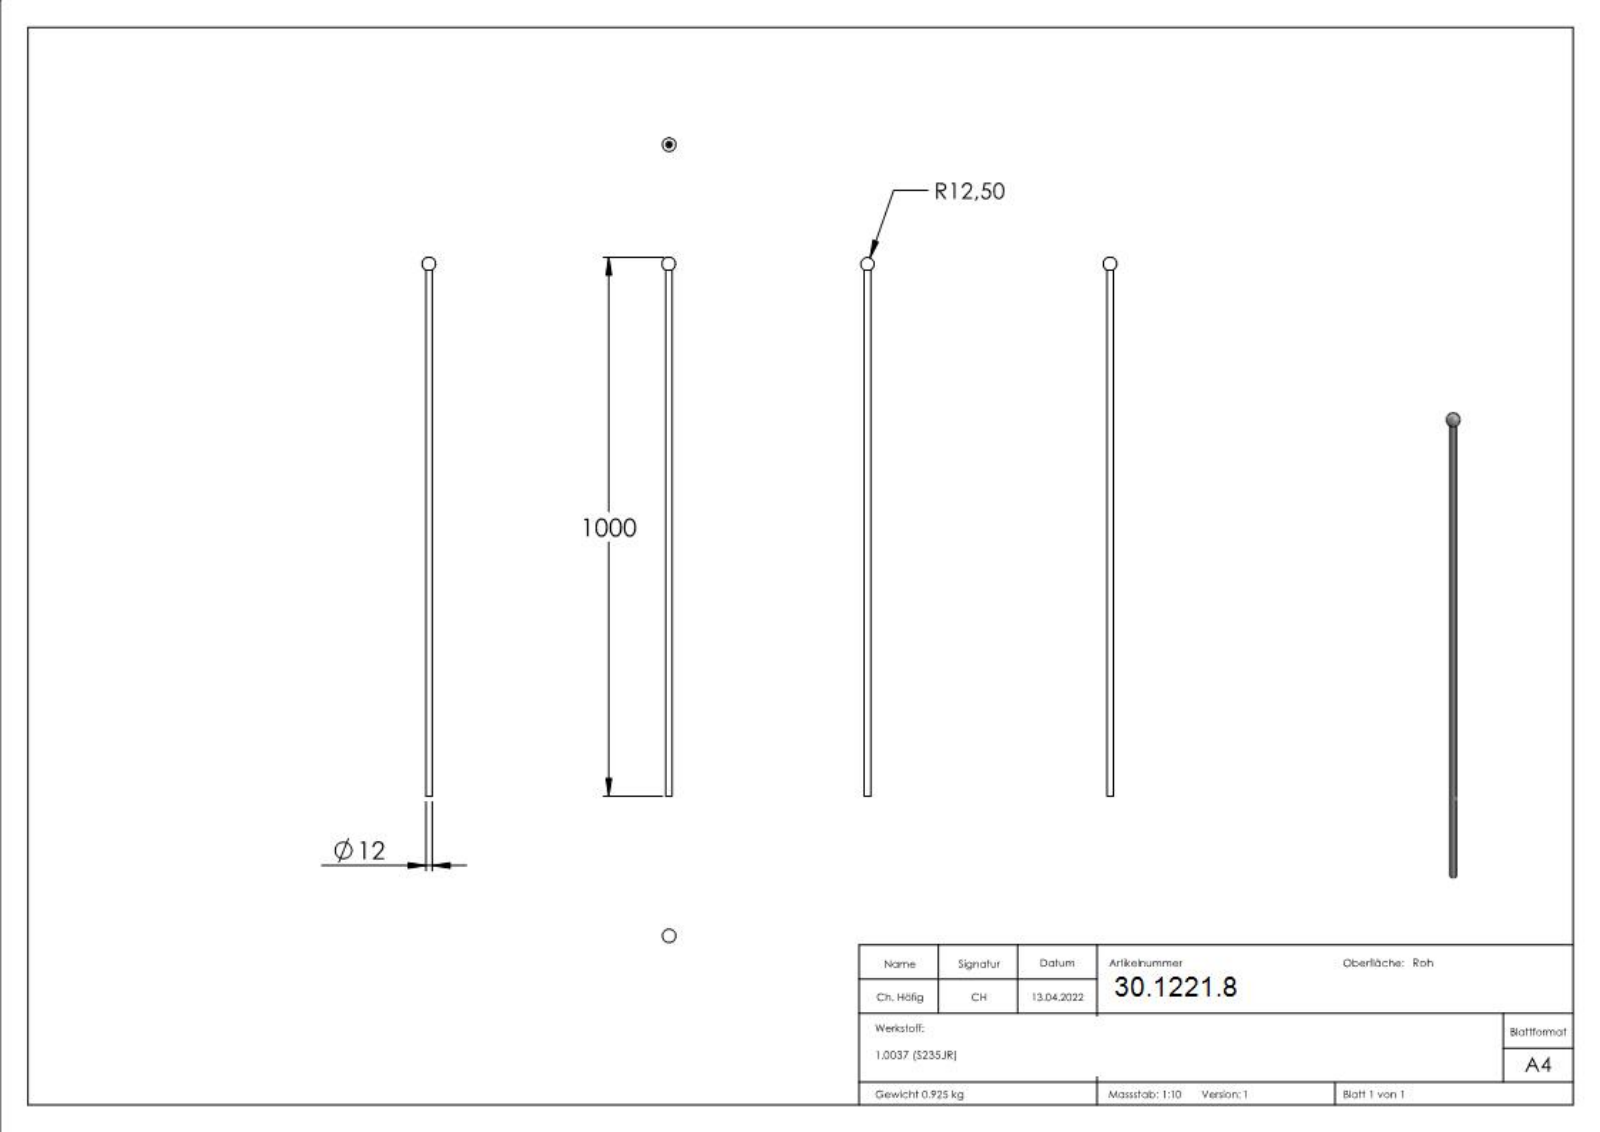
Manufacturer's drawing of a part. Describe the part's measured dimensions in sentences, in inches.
The part is named "1306-IT". Its 3-D file was written by "SolidWorks 2018 (CONFIG_CONTROL_DESIGN)". It is 1 solid with 228 faces: 126 planar, 1 cylindrical and 101 other. Overall it measures 39.37 by 0.984 by 0.984 inches. Its volume is 7.234 cubic inches and its surface area 60.1 square inches. Round bosses or shafts: 1 of diameter 0.472. The main face-to-face distances are 0.069, 0.091, 0.019, 0.089, 0.077, 0.019, 0.076, 0.103, 0.096, 0.029.
